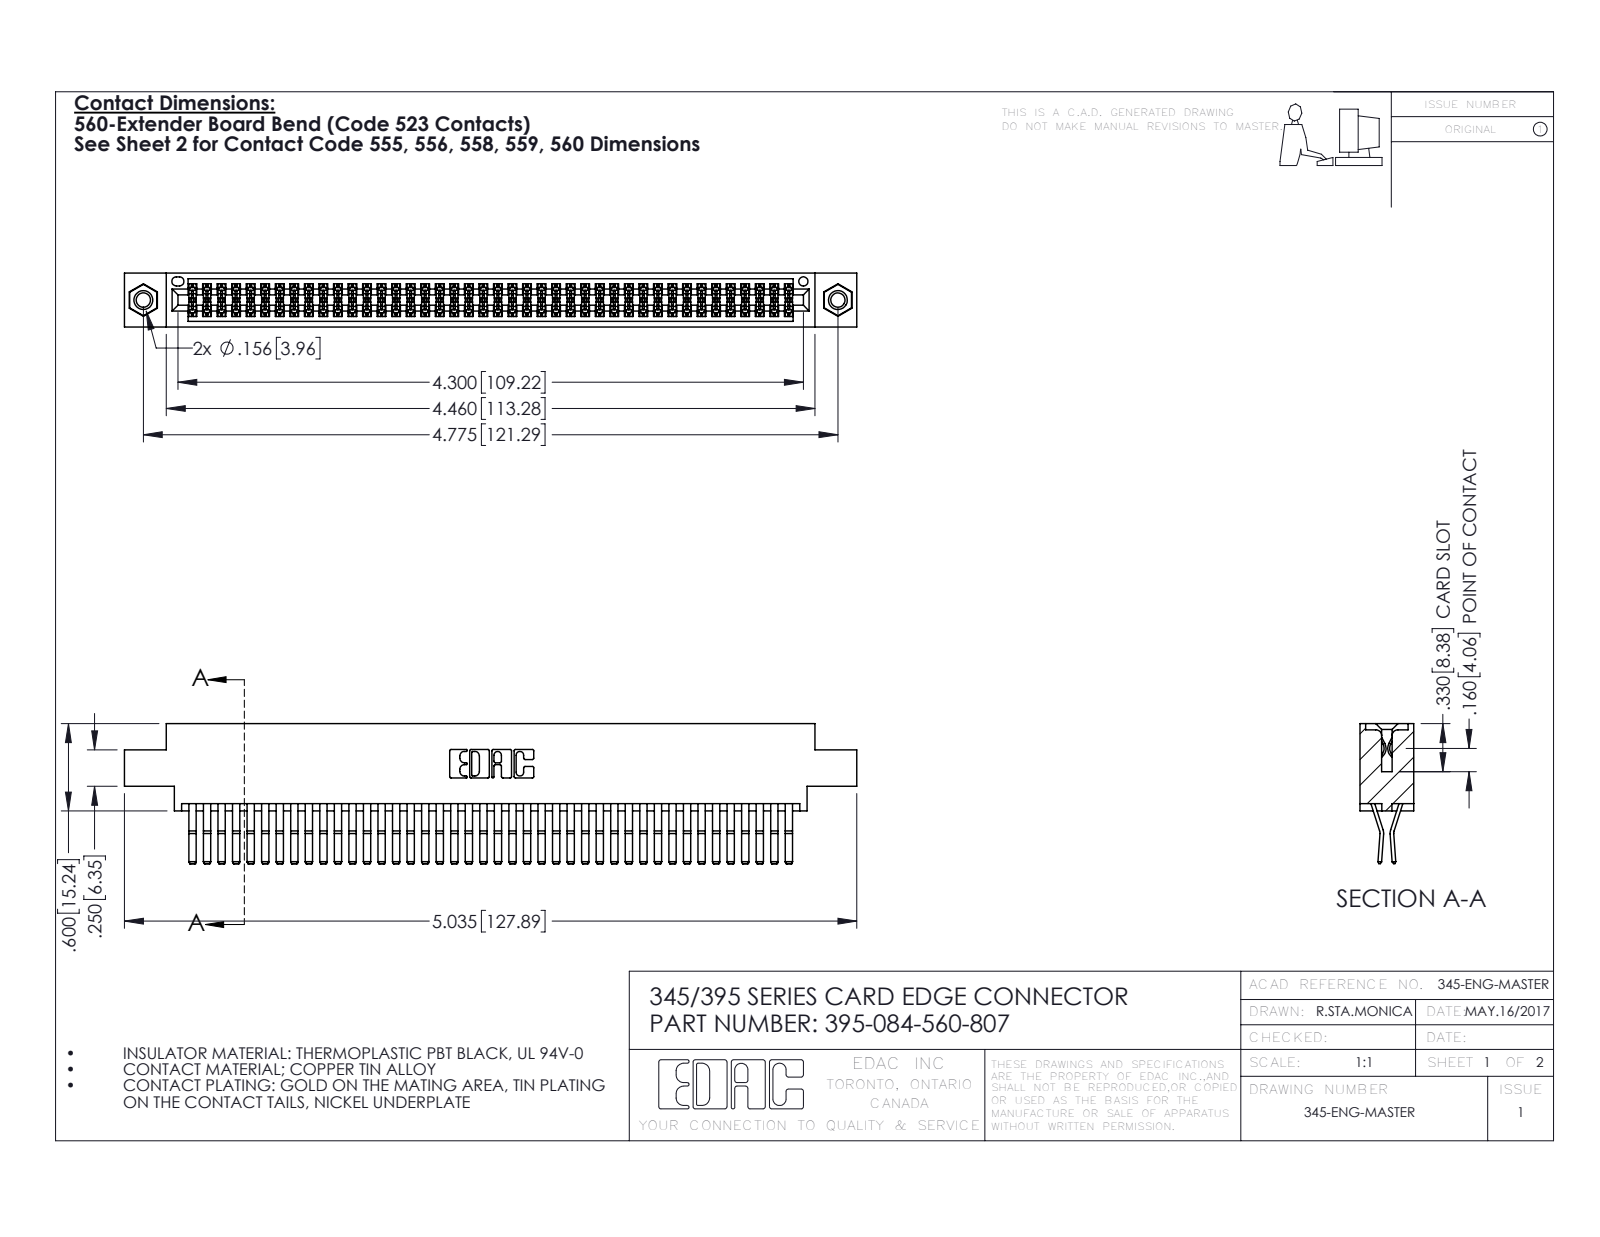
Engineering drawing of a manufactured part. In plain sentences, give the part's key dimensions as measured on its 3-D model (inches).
The part is named "395-084-560-807; 345-292-001_560 Tail; 345-250-001_345-250-005-103; 345 Part_0.170 Offset - 0.156 Dia-TI". Its 3-D file was written by "SolidWorks 2016 (CONFIG_CONTROL_DESIGN)". It is 87 solids with 4558 faces: 2888 planar, 1654 cylindrical and 16 other. Overall it measures 5.035 by 0.962 by 0.37 inches. Its volume is 0.784 cubic inches and its surface area 31.89 square inches. Round holes: 2 of diameter 0.098, 2 of diameter 0.125, 2 of diameter 0.156, 1 of diameter 0.064. Round bosses or shafts: 2 of diameter 0.155. Partial cylindrical surfaces (rounded edges, fillets, slot ends): 127 of radius 0.006, 22 of radius 0.01, 6 of radius 0.007, 6 of radius 0.031, 3 of radius 0.026, 2 of radius 0.01, 2 of radius 0.014, 2 of radius 0.019. The main face-to-face distances are 0.025, 0.072, 0.298, 0.37, 0.2, 0.098, 0.272, 0.225, 0.175, 0.149. The hole center spacings are 0.27, 4.539, 4.775.
